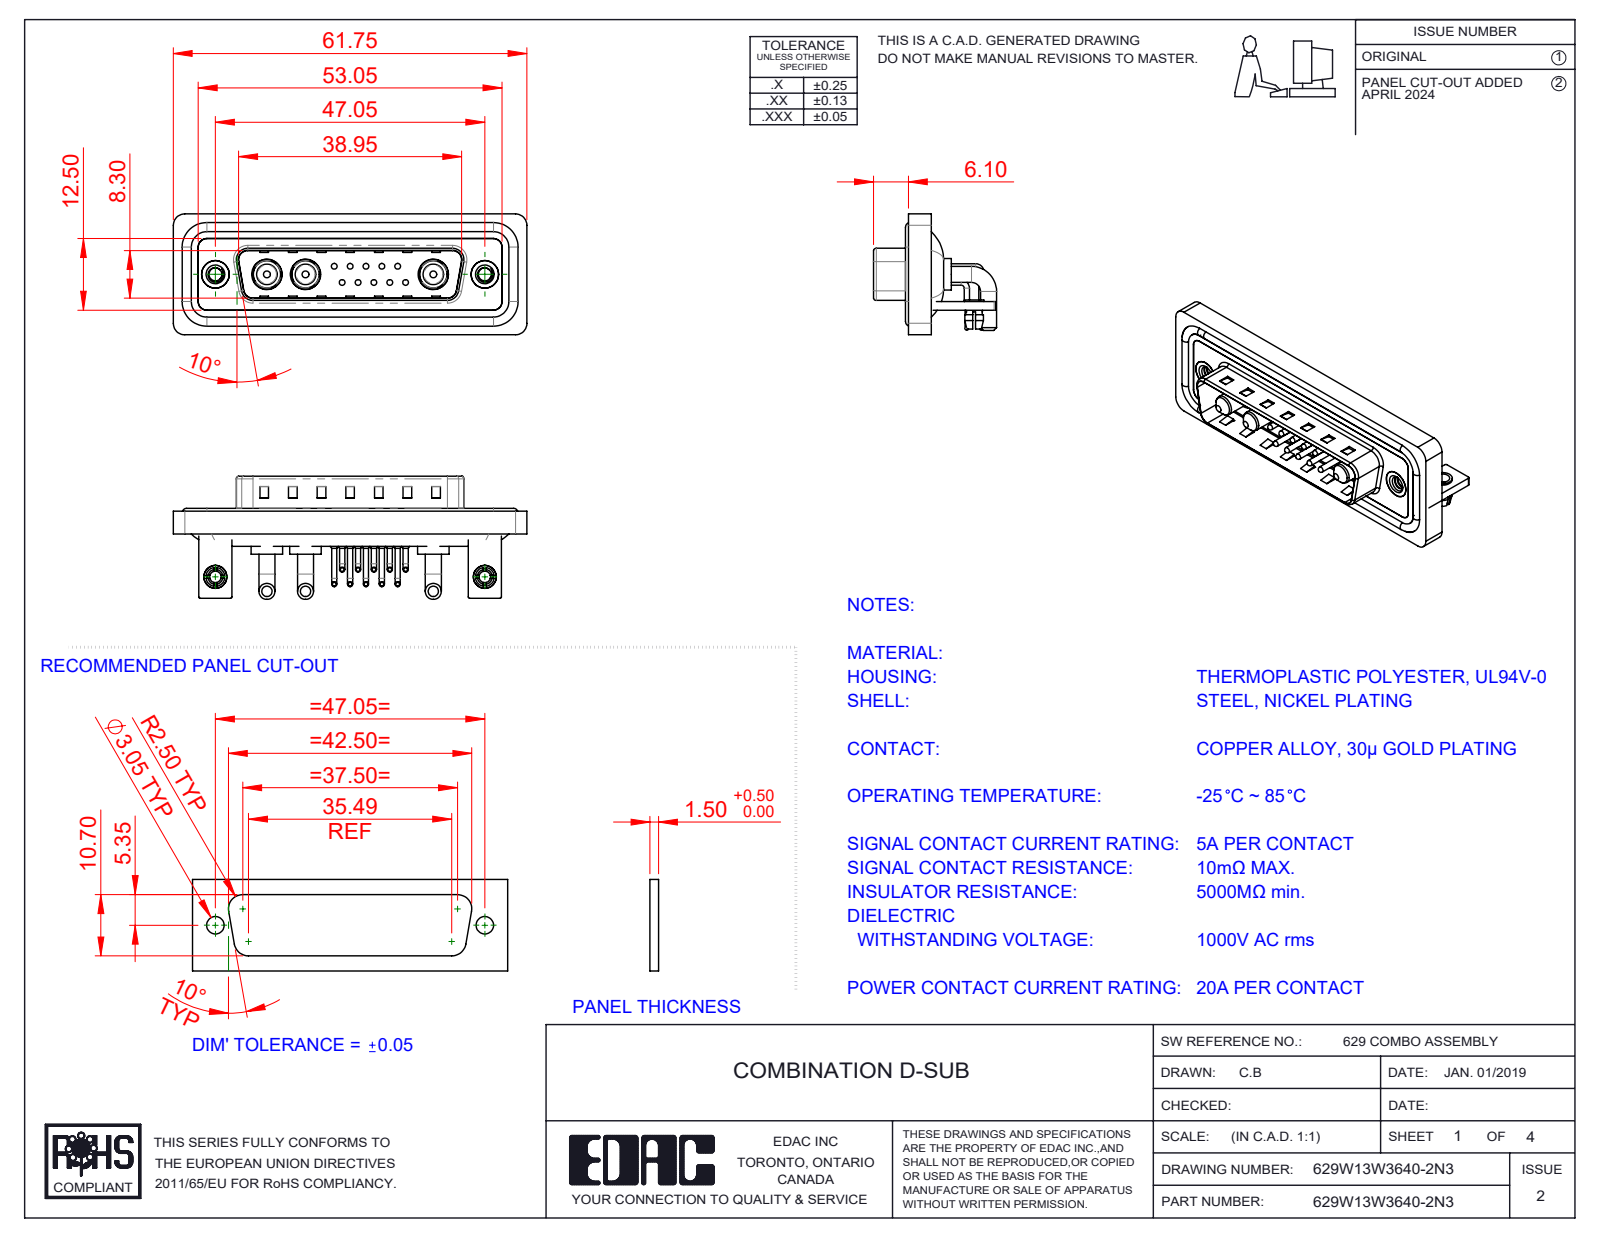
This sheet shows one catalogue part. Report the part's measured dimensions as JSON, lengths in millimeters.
{"part_name": "629Combo Housing_13W3; 629Combo Shell Rear_25 Contacts; 629Combo Waterproof Housing_25 Contacts; 629Combo Board Lock (+7 more)", "step_written_by": "SolidWorks 2023 (CONFIG_CONTROL_DESIGN)", "units": "millimeters", "bodies": {"solids": 27, "faces": 1844, "planar": 947, "cylindrical": 661, "other": 236}, "overall_size": [61.75, 21.5, 21.1], "volume_mm3": 7924, "surface_area_mm2": 13293, "round_holes": [[2, 12], [0.75, 10], [1.6, 10], [4.85, 3], [5.3, 3], [2.26, 2], [2.5, 2], [3.2, 2], [4, 2], [4.8, 2], [5, 2]], "round_bosses_or_shafts": [[0.9, 20], [1.5, 10], [1, 10], [0.65, 10], [2.8, 6], [1.6, 4], [5.5, 3], [5.2, 3]], "partial_cylinders_radius": [[2, 19], [1.5, 18], [0.25, 16], [1.01, 10], [0.5, 9], [1.6, 8], [0.6, 4], [0.65, 4]], "face_to_face_distances": [0.4, 0.8, 1.5, 2.9, 2.1, 1.1, 4.1, 1.6, 3.7, 4.5], "hole_center_spacings": [3.16, 2.77, 5.04, 5.54, 7.49, 5.03, 8.31, 10.11]}
